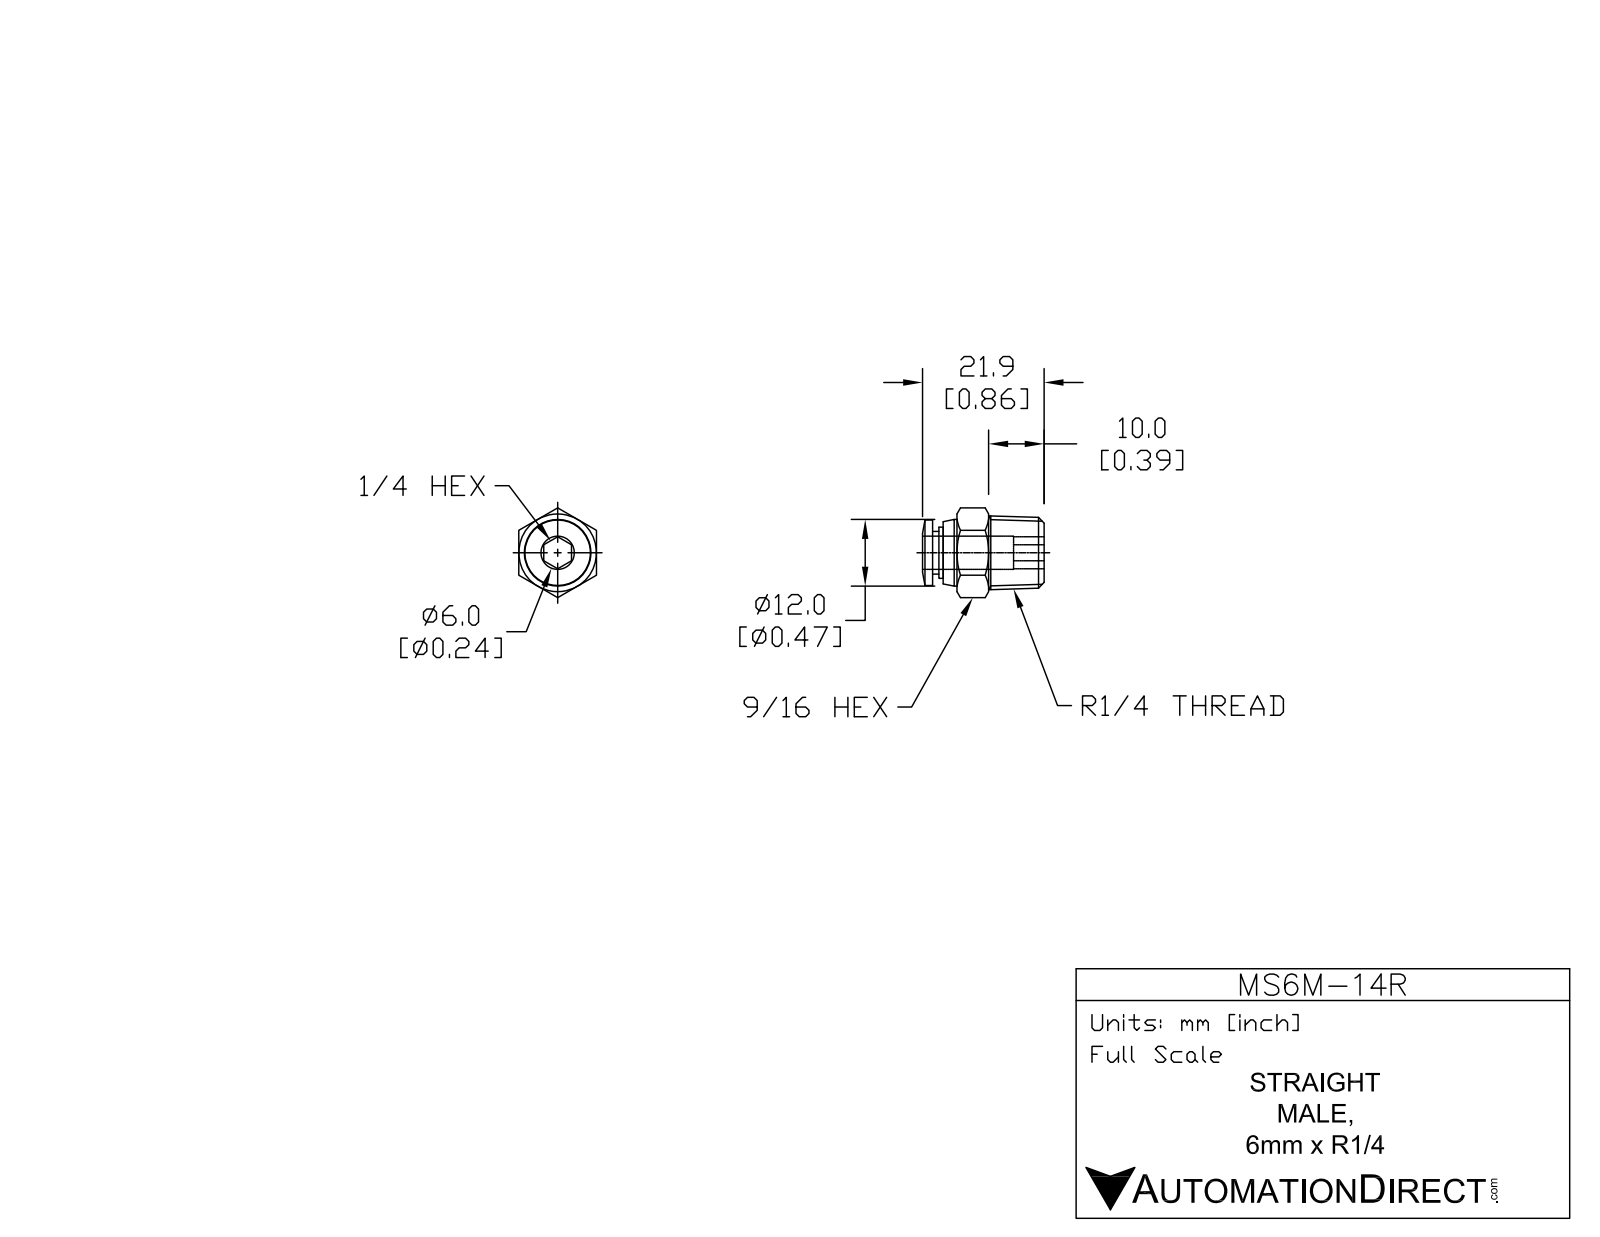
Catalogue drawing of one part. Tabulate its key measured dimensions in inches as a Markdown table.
| quantity | value |
| --- | --- |
| part name | MS6M-14R |
| STEP written by | SolidWorks 2015 (AUTOMOTIVE_DESIGN) |
| units | inches |
| bodies | 1 solid, 50 faces (14 planar, 12 cylindrical, 24 other) |
| overall size | 0.862 × 0.636 × 0.551 |
| volume | 0.134 in³ |
| surface area | 2.554 in² |
| round holes (diameter × count) | 0.197 × 1, 0.248 × 1 |
| round bosses / shafts (diameter × count) | 0.472 × 1, 0.465 × 1, 0.362 × 1, 0.303 × 1 |
| main face-to-face distances | 0.551, 0.791, 0.618, 0.173, 0.717, 0.098, 0.075, 0.746, 0.128, 0.03 |
